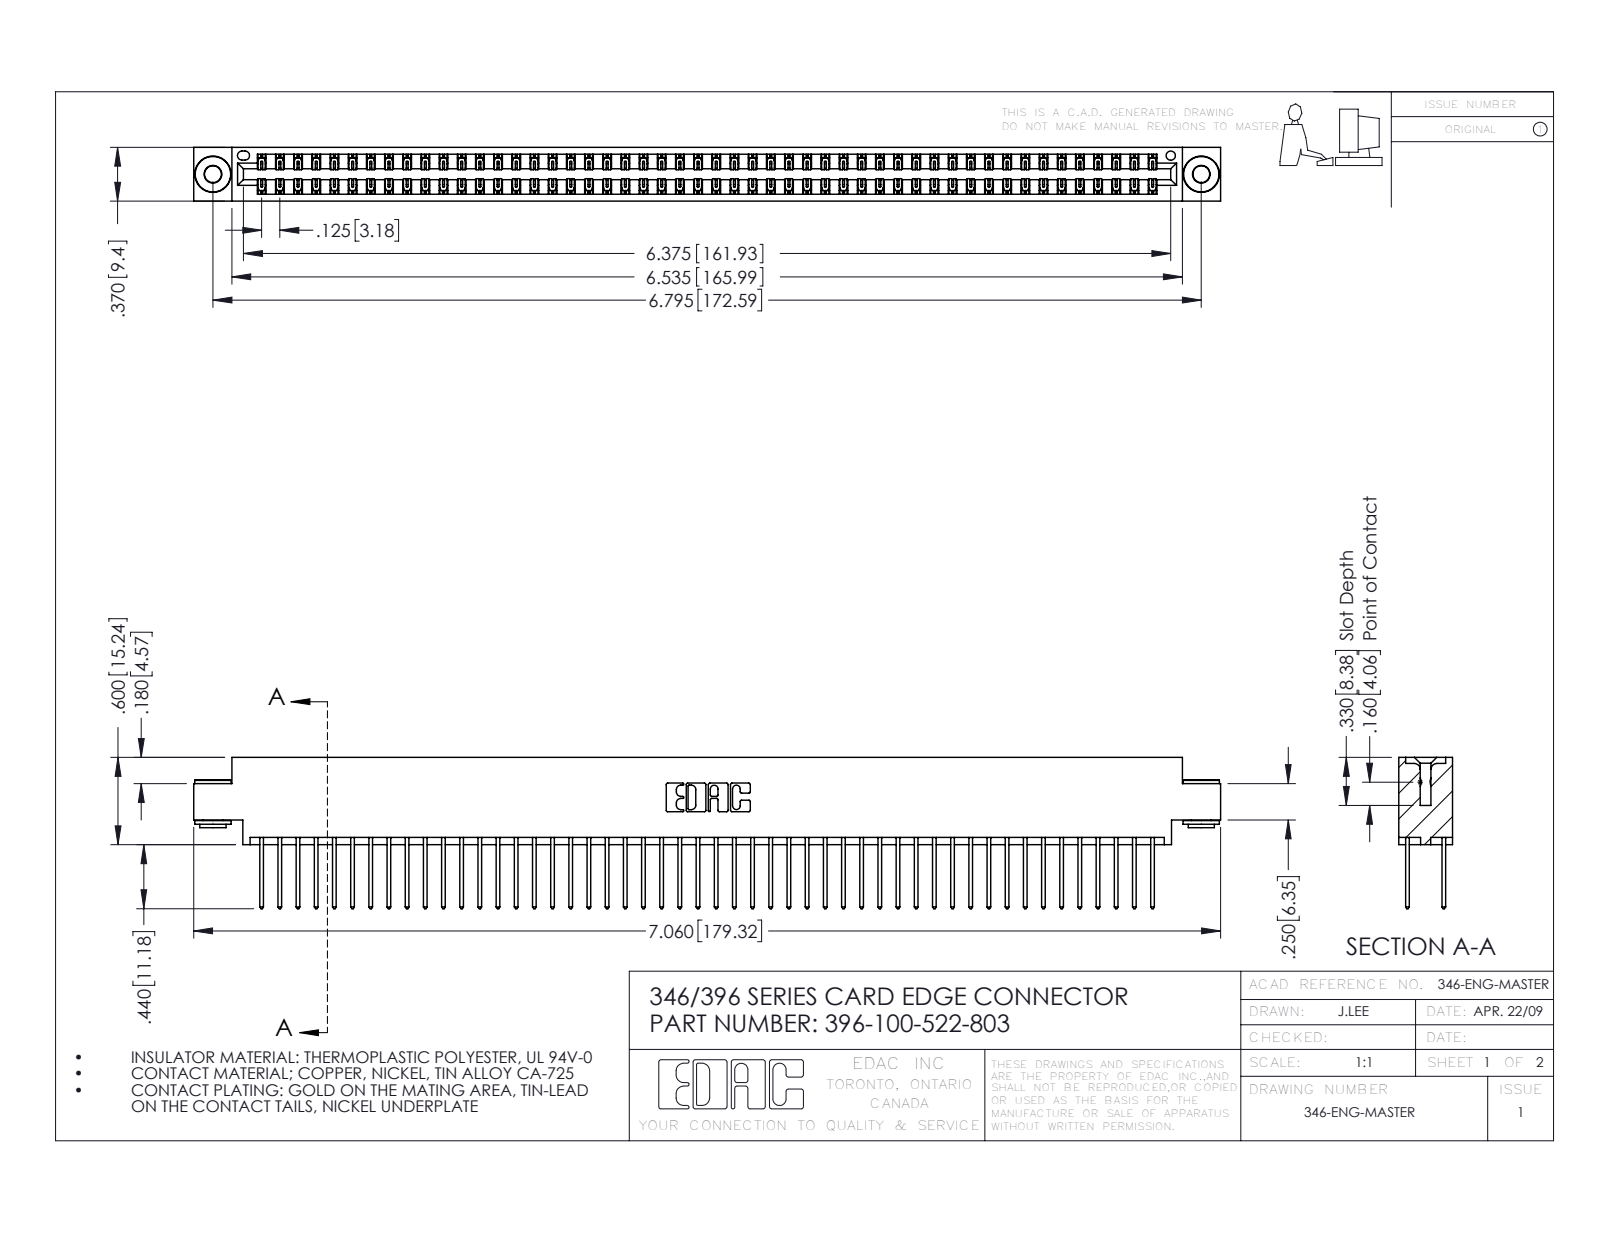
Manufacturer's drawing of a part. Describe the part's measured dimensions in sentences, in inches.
The part is named "396-100-522-803; 346 Part_0.170 Offset - 0.156 Dia-TH; 345-250-002_345-250-002-102; 345-292-001_345-293-122". Its 3-D file was written by "SolidWorks 2016 (CONFIG_CONTROL_DESIGN)". It is 103 solids with 5364 faces: 3590 planar, 1766 cylindrical and 8 other. Overall it measures 7.06 by 1.04 by 0.37 inches. Its volume is 1.078 cubic inches and its surface area 40.29 square inches. Round holes: 2 of diameter 0.116, 2 of diameter 0.156, 1 of diameter 0.064. Round bosses or shafts: 2 of diameter 0.25, 2 of diameter 0.18, 2 of diameter 0.136. Partial cylindrical surfaces (rounded edges, fillets, slot ends): 150 of radius 0.006, 100 of radius 0.01, 22 of radius 0.01, 6 of radius 0.007, 6 of radius 0.031, 3 of radius 0.026, 2 of radius 0.014, 2 of radius 0.022. The main face-to-face distances are 0.048, 0.322, 0.25, 0.37, 0.025, 0.072, 0.298, 0.275, 0.148, 0.222. The hole center spacings are 0.246, 6.586, 6.795.
